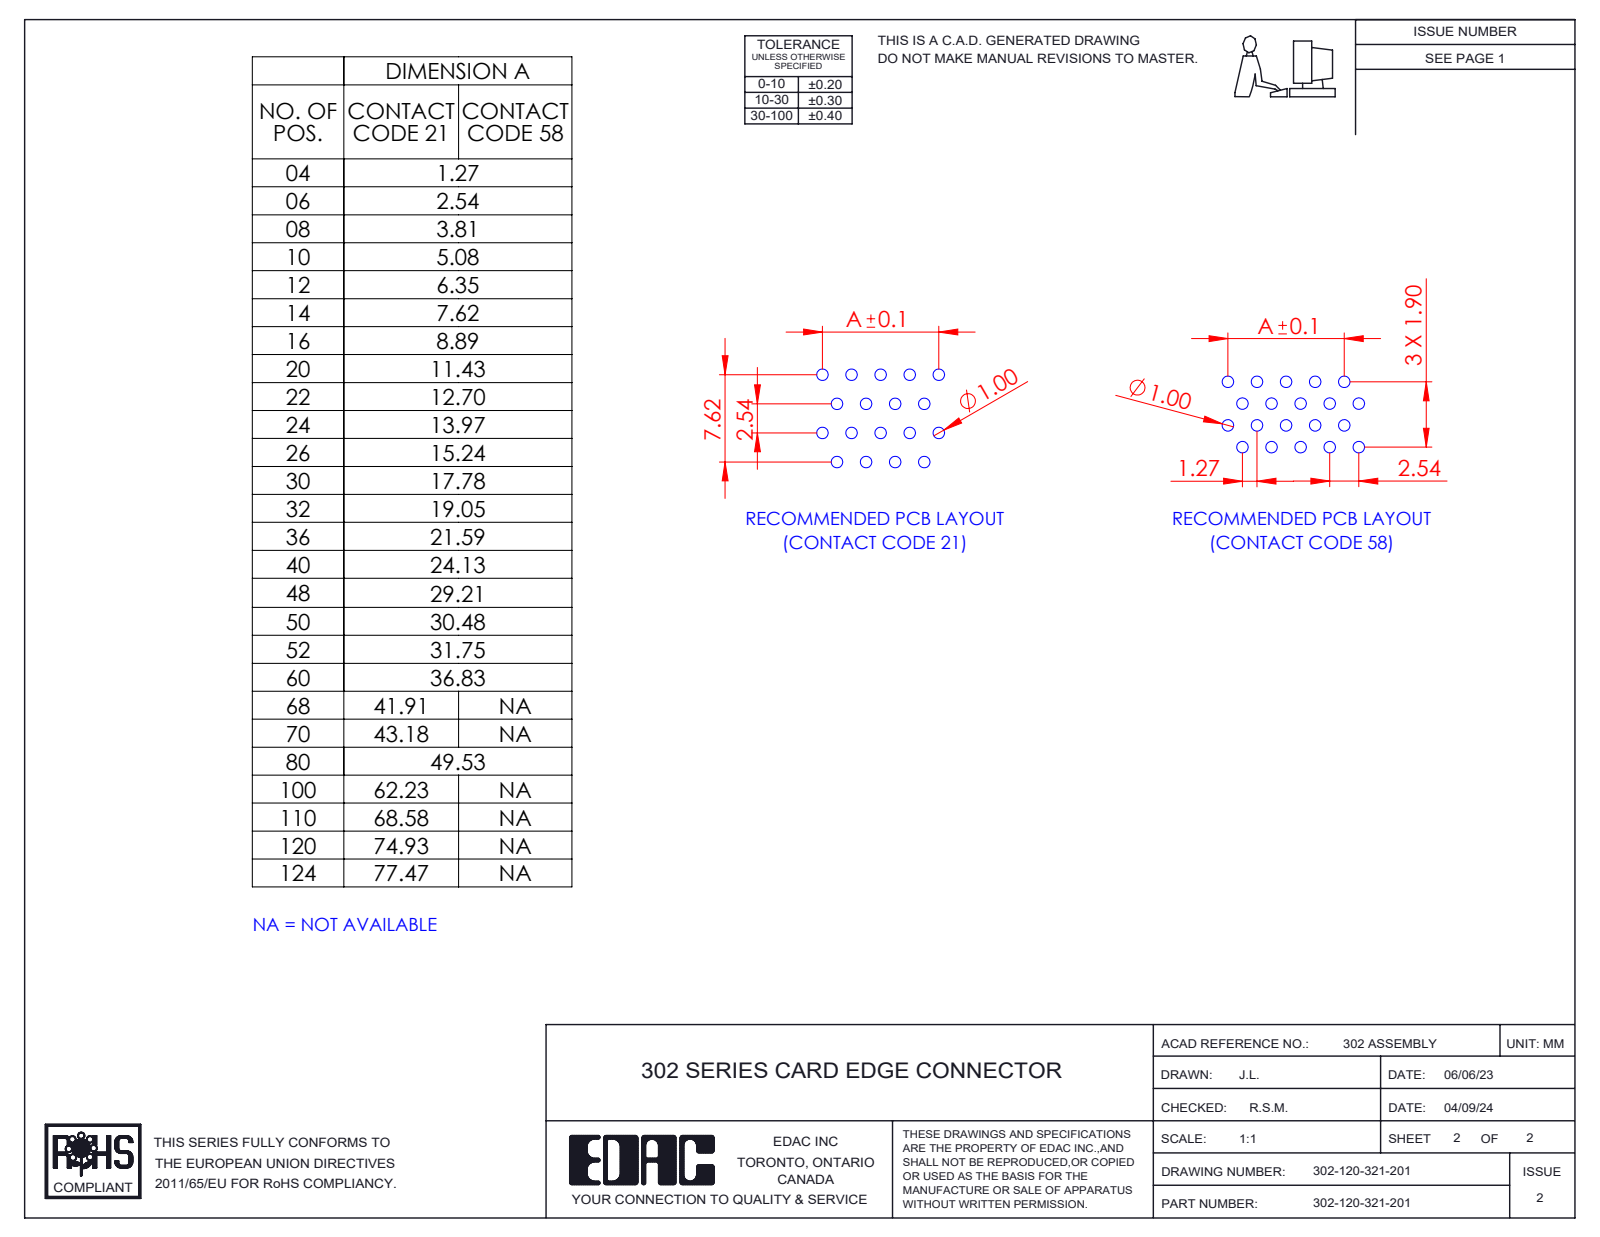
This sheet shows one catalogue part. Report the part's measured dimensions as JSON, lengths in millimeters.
{"part_name": "Contact_302-290-X21 (2); Contact_302-290-X21 (1); HSG_Vertical HSG; 302-120-321-201", "step_written_by": "SolidWorks 2023 (CONFIG_CONTROL_DESIGN)", "units": "millimeters", "bodies": {"solids": 121, "faces": 5526, "planar": 4069, "cylindrical": 1213, "other": 244}, "overall_size": [82.3, 17.63, 8.88], "volume_mm3": 6254, "surface_area_mm2": 17951, "partial_cylinders_radius": [[0.2, 128], [2.03, 4], [2.09, 4], [0.11, 2], [0.4, 2], [0.41, 2], [1.25, 2], [1.53, 2]], "face_to_face_distances": [8.88, 2.54, 5.08, 3.8, 7.62, 3.49, 5.39, 1.9, 10.16, 6.34]}
